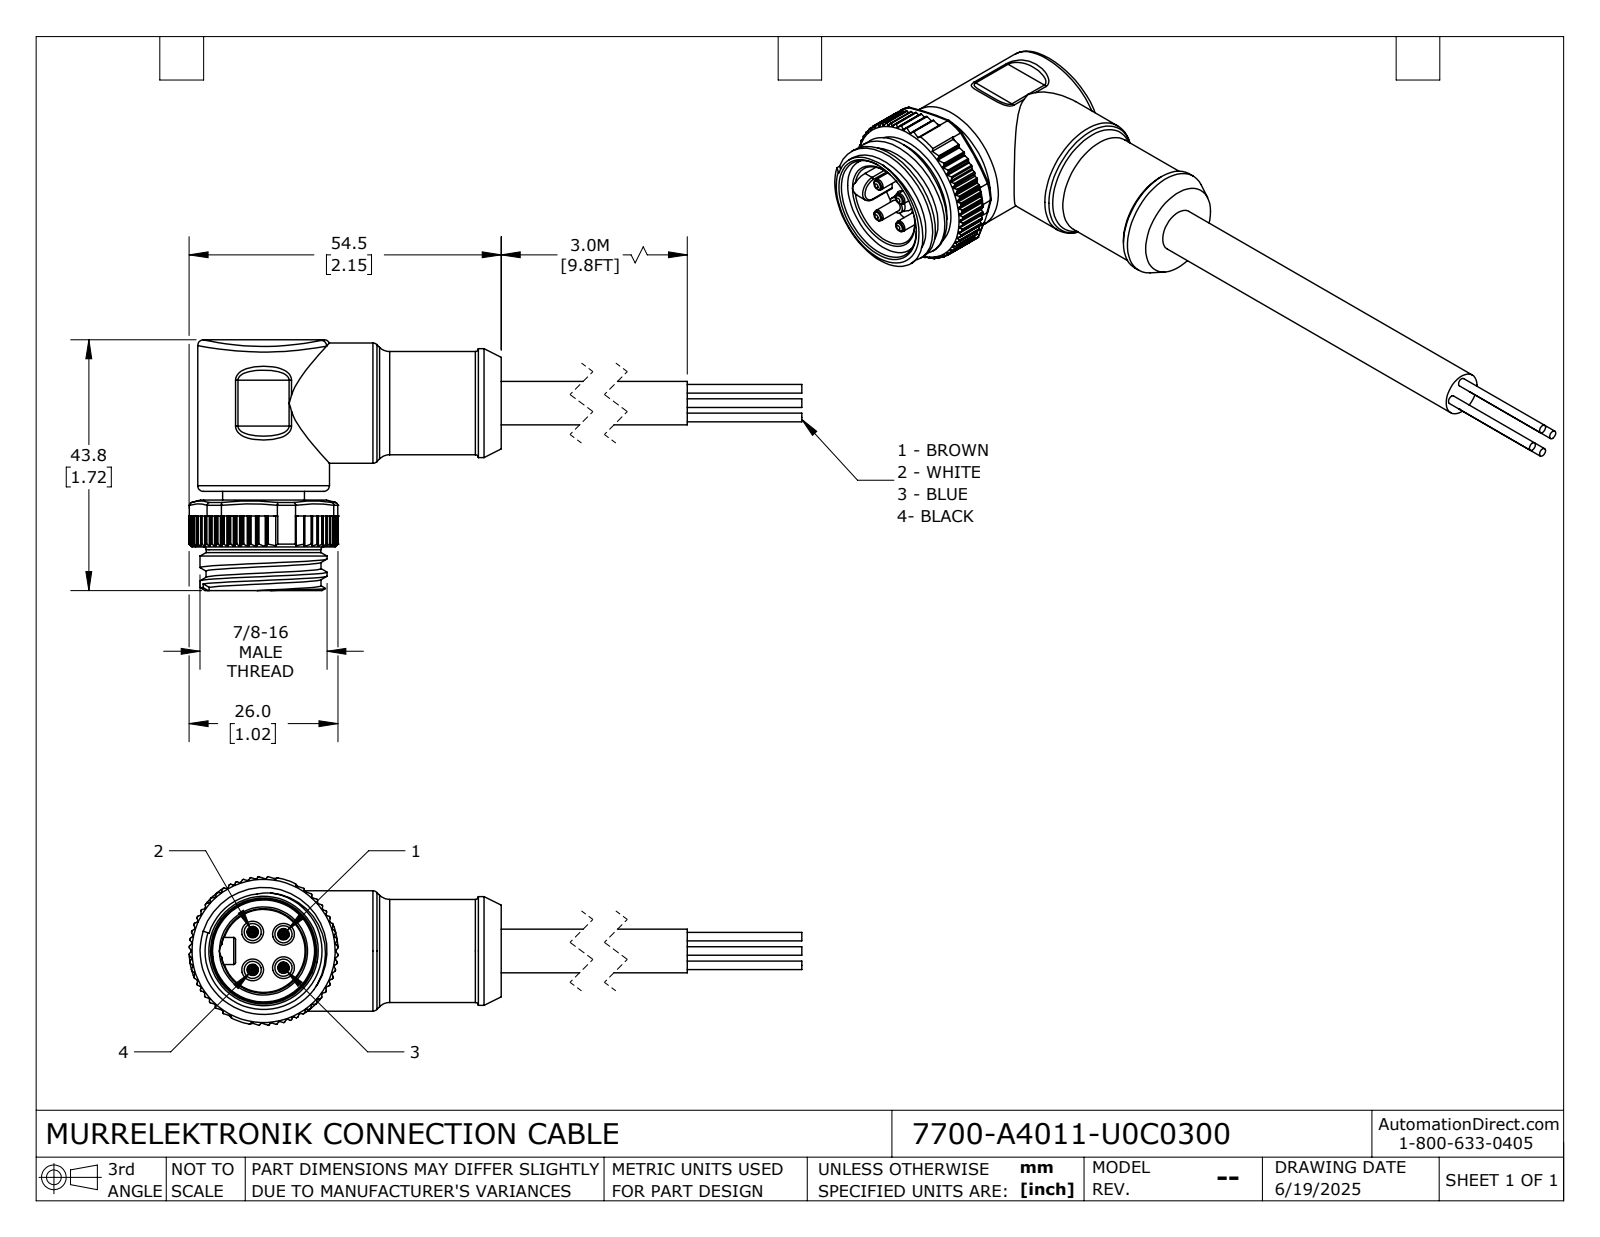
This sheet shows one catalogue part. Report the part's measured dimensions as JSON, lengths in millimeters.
{"part_name": "7700-A4011-U0C0300", "step_written_by": "SolidWorks 2024 (CONFIG_CONTROL_DESIGN)", "units": "millimeters", "bodies": {"solids": 1, "faces": 604, "planar": 238, "cylindrical": 282, "other": 84}, "overall_size": [144.49, 43.76, 25.95], "volume_mm3": 28280, "surface_area_mm2": 10856, "round_holes": [[15.6, 1], [18.5, 1]], "round_bosses_or_shafts": [[3, 4], [2, 4], [1.5, 4], [23, 1], [22.17, 1], [21, 1], [20.05, 1], [20, 1]], "partial_cylinders_radius": [[0.2, 126], [0.3, 18], [0.1, 4], [0.7, 4], [1, 4], [2.5, 4], [2.35, 1], [13, 1]], "face_to_face_distances": [1.5, 8.2, 9.7, 0.9, 7.3, 8.8, 15.8, 21, 14.3, 6.1]}
